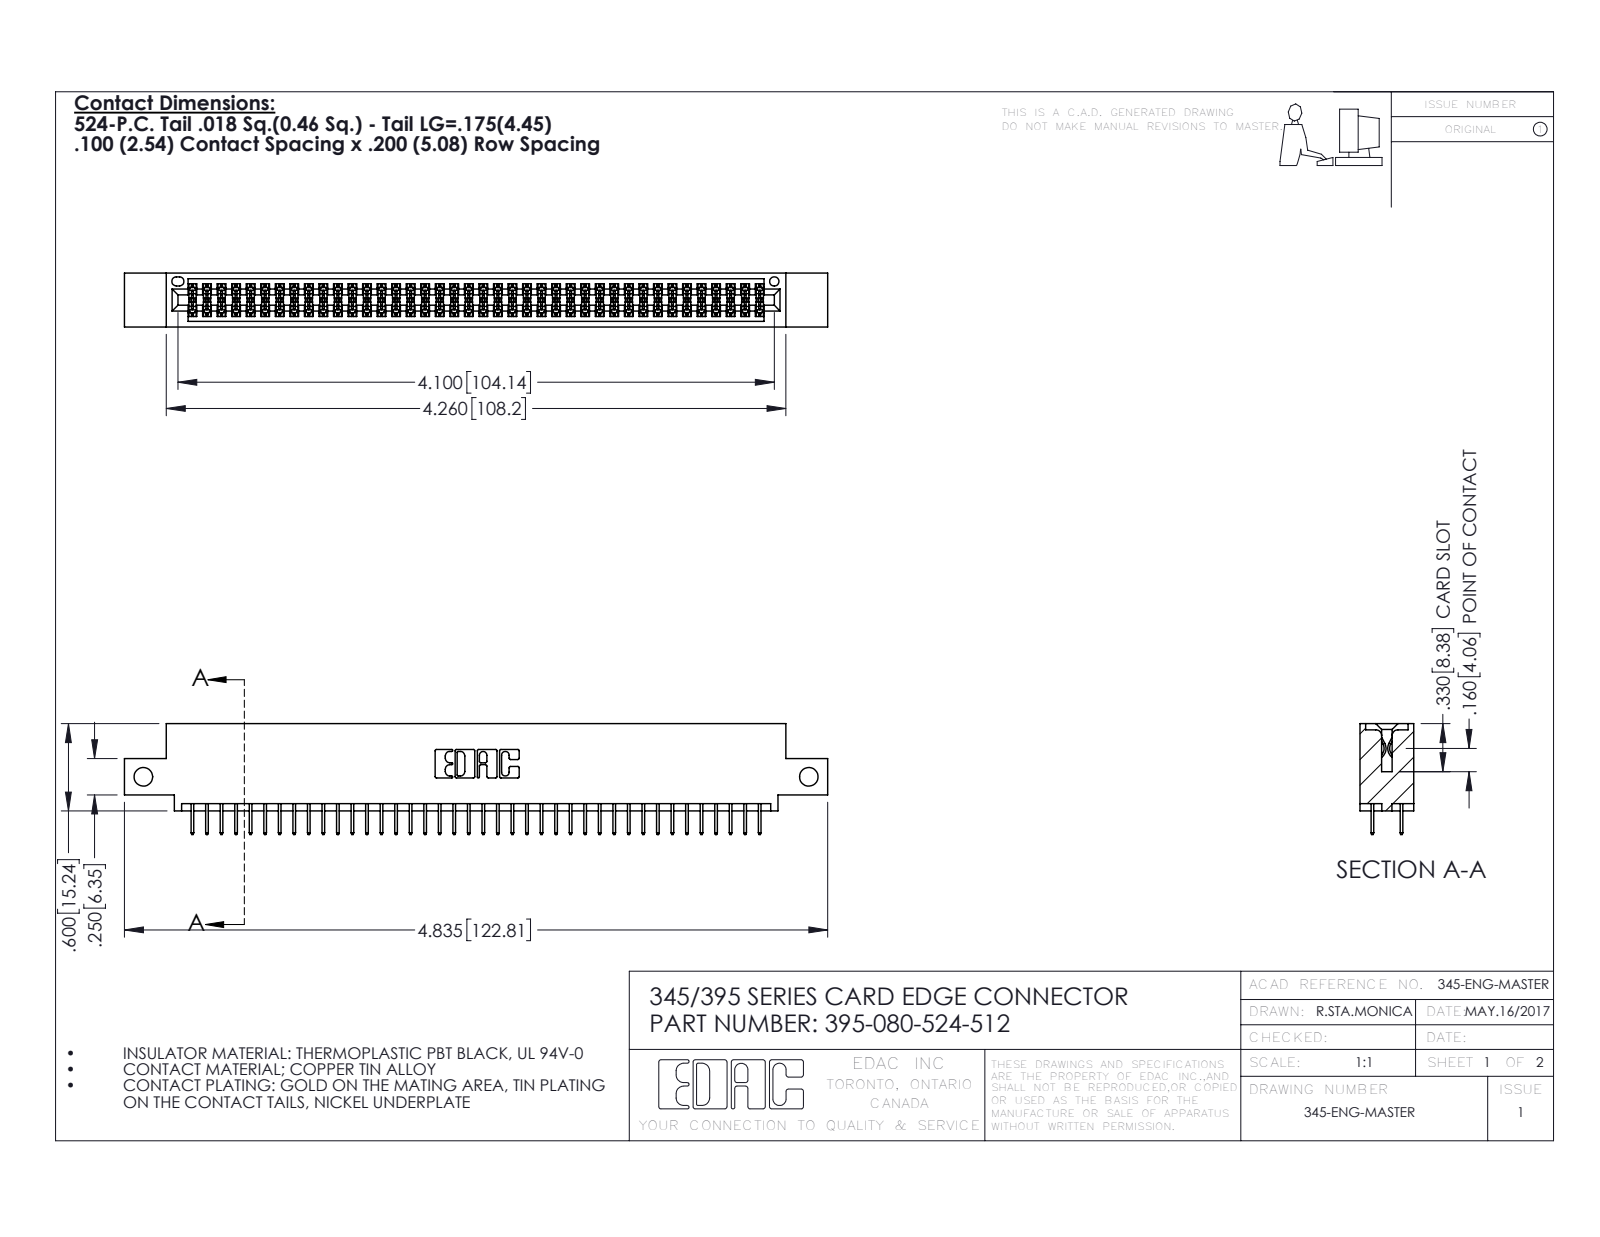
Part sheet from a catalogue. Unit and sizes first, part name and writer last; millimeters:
Units: millimetres
Overall size (bounding box): 122.8 × 19.4 × 9.4
Round holes (diameter × count): ⌀3.3 ×2, ⌀1.6 ×1
Partial cylindrical surfaces — rounded edges, fillets, slot ends (radius × count): R0.2 ×120, R0.3 ×22, R0.2 ×6, R0.8 ×6, R0.7 ×3, R0.4 ×2, R0.5 ×2, R0.6 ×2
Main face-to-face distances: 1.8, 7.6, 5.1, 9.4, 2.5, 6.9, 0.6, 5.7, 1.8, 4.4
Hole centre spacings: 116.2
Volume: 11 600 mm³ · Surface area: 16 790 mm²
Bodies: 81 solids, 4450 faces (3204 planar, 1246 cylindrical, 0 other)
Part name (STEP PRODUCT): 345 Part_0.110 Offset - Side Mount; 345-292-001_345-293-124; 395-080-524-512
STEP written by: SolidWorks 2016 (CONFIG_CONTROL_DESIGN)
